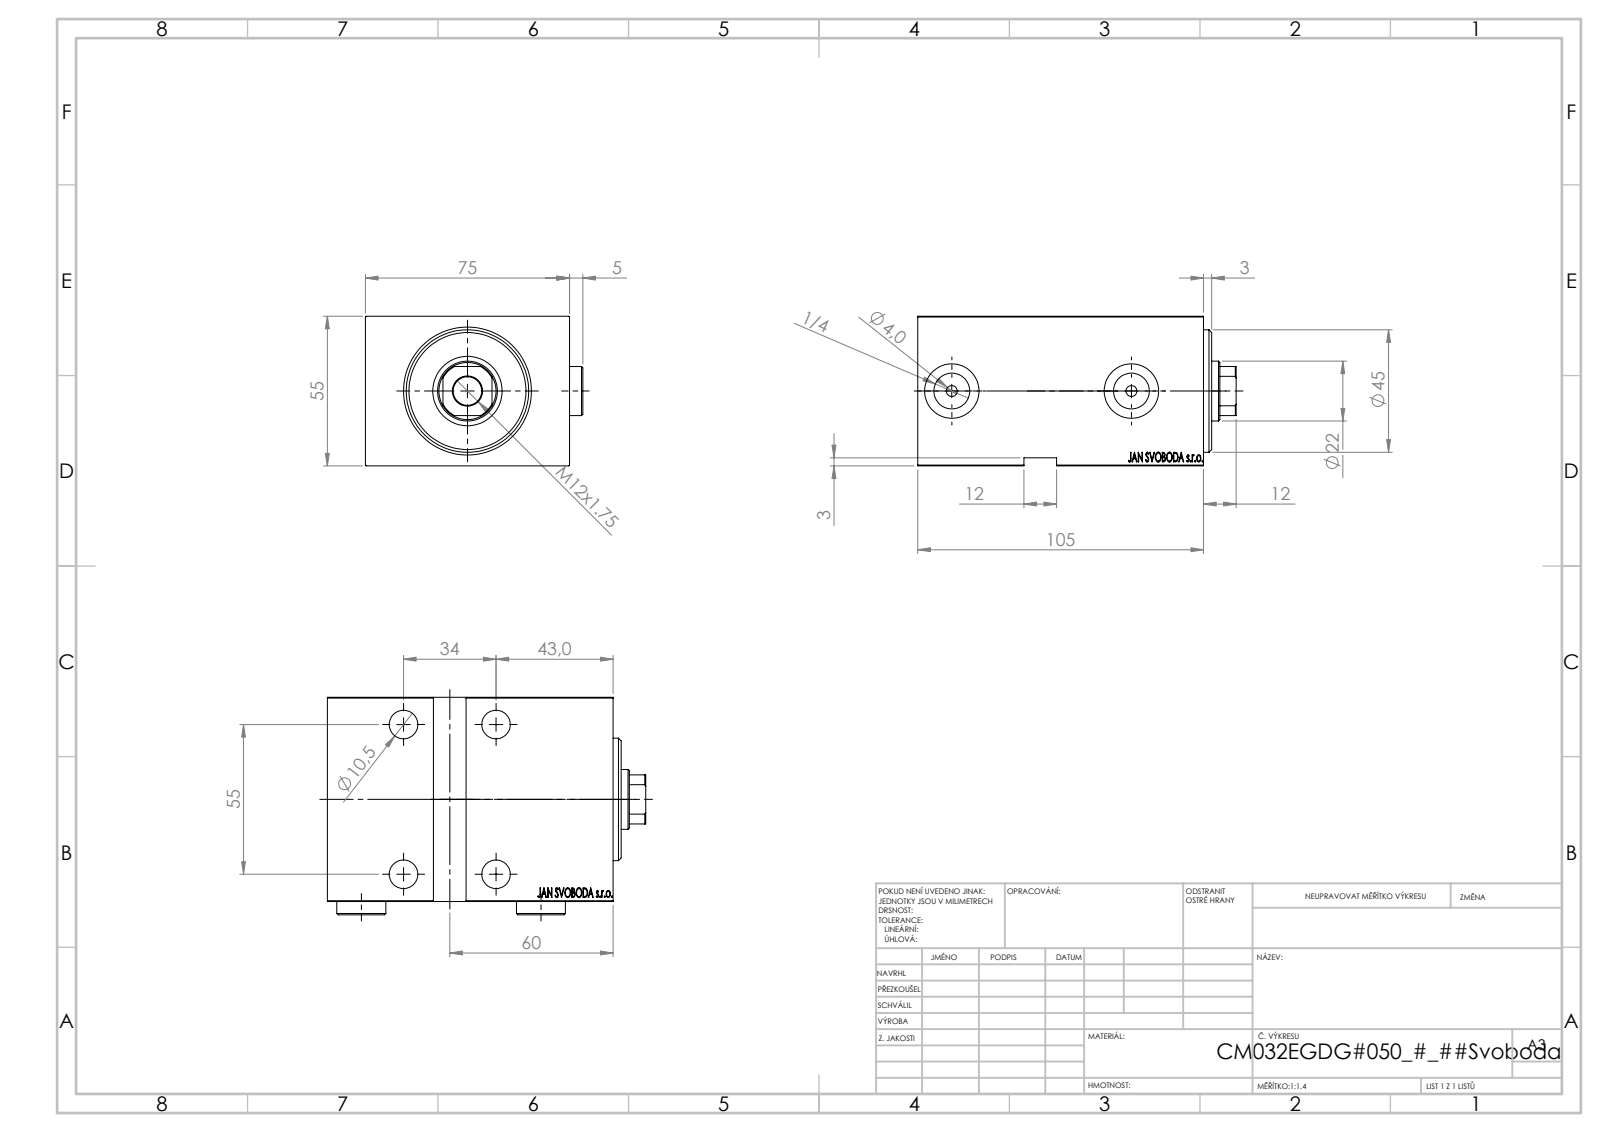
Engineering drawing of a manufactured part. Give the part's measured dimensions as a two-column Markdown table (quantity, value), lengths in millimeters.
| quantity | value |
| --- | --- |
| part name | Zatka_OIL_PORT; V450CM_E_VCP; V450CM_VC_B; V450CM_E_Body |
| STEP written by | SolidWorks 2019 (CONFIG_CONTROL_DESIGN) |
| units | millimeters |
| bodies | 5 solids, 909 faces (445 planar, 66 cylindrical, 398 other) |
| overall size | 117 × 79.9 × 55 |
| volume | 385 678 mm³ |
| surface area | 74 277 mm² |
| round holes (diameter × count) | 10.5 × 5, 16.5 × 4, 4 × 2, 13.16 × 2, 20 × 2, 22 × 1, 25.5 × 1, 32 × 1, 45 × 1 |
| round bosses / shafts (diameter × count) | 18 × 2, 34 × 1 |
| partial cylindrical surfaces (radius × count) | 10.5 × 1 |
| main face-to-face distances | 55, 75, 105, 3, 5, 10, 95, 100, 90, 74.9 |
| hole center spacings | 34, 55, 64.66, 66 |
